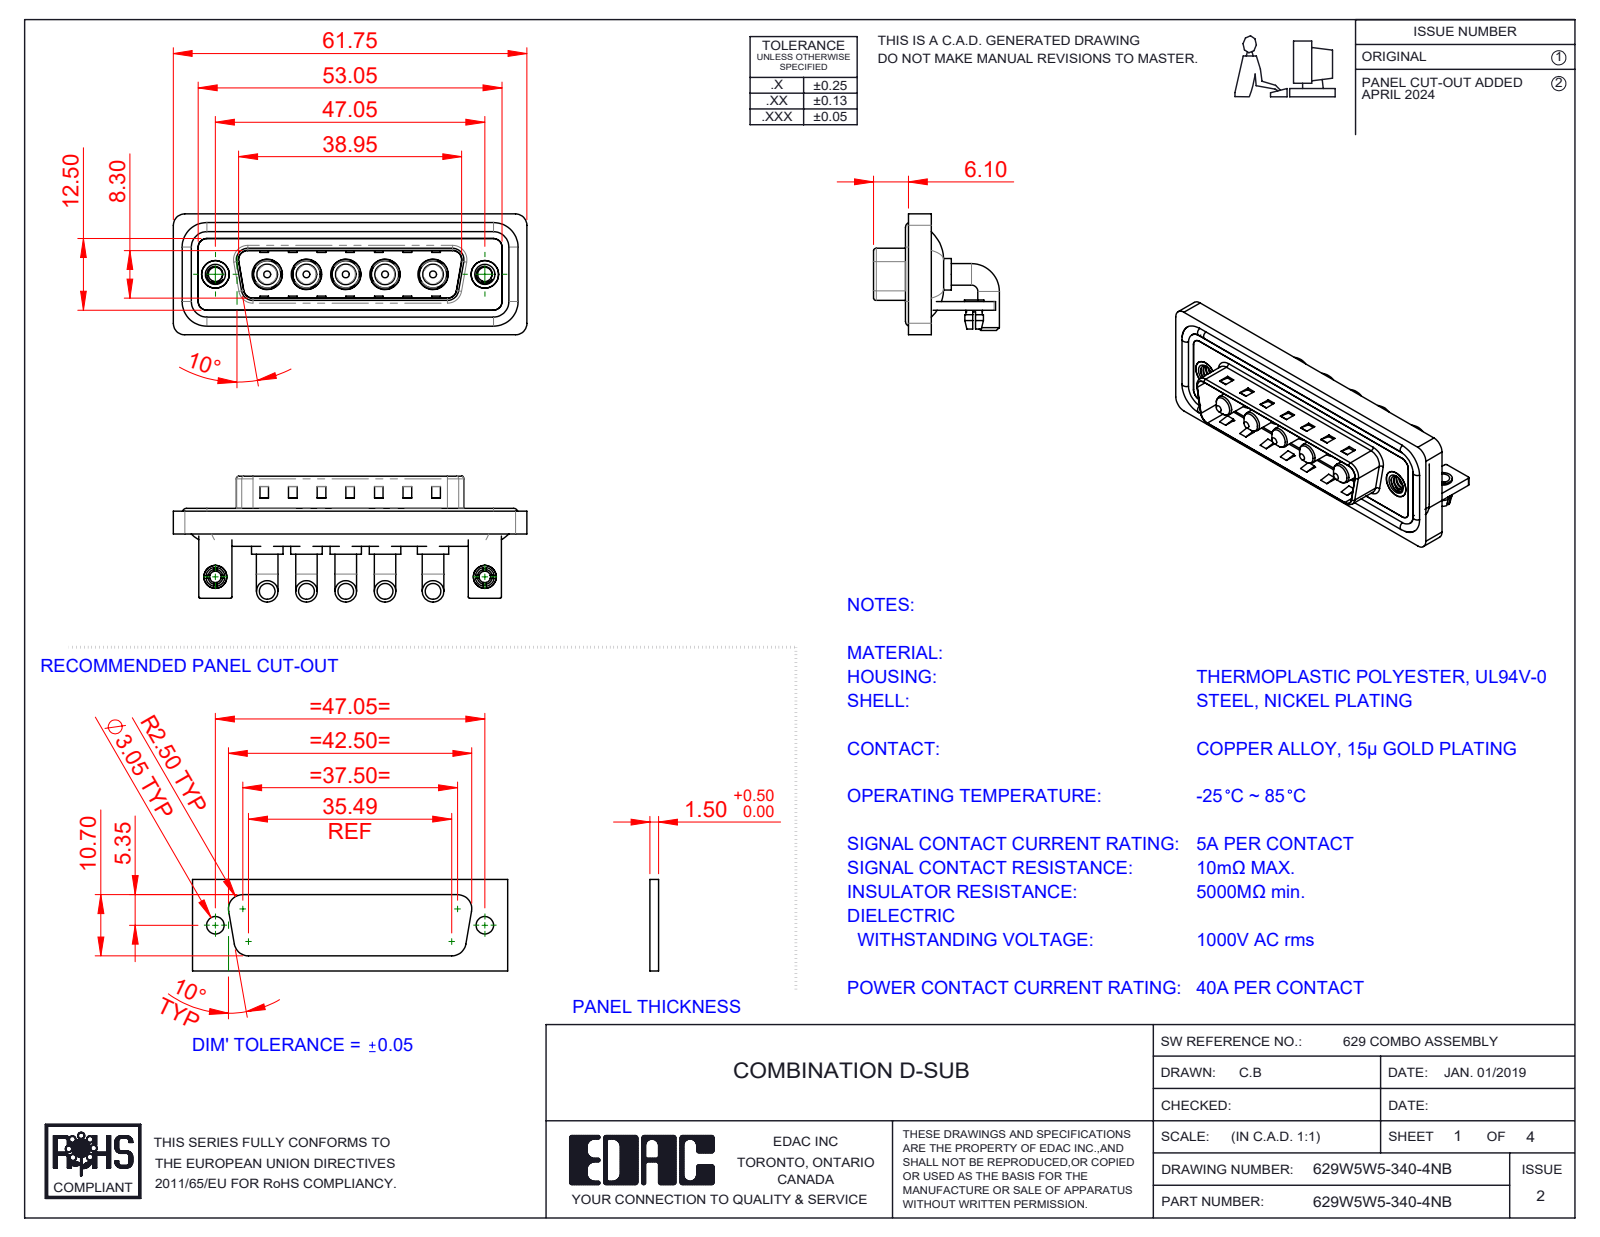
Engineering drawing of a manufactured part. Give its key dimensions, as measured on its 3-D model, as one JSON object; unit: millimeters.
{"part_name": "629Combo Stabilizer Bracket; 629Combo Housing_5W5; 629Combo Waterproof Housing_25 Contacts; 629Combo Shell Rear_25 Contacts (+5 more)", "step_written_by": "SolidWorks 2023 (CONFIG_CONTROL_DESIGN)", "units": "millimeters", "bodies": {"solids": 21, "faces": 828, "planar": 327, "cylindrical": 343, "other": 158}, "overall_size": [61.75, 21.98, 21.1], "volume_mm3": 8475, "surface_area_mm2": 13290, "round_holes": [[4.85, 5], [5.3, 5], [2.5, 4], [2, 2], [3.2, 2], [4, 2], [4.8, 2], [5, 2]], "round_bosses_or_shafts": [[3.75, 10], [5.5, 5], [5.2, 5], [4.75, 5], [3.6, 5], [1.6, 4], [4.9, 2], [4, 2]], "partial_cylinders_radius": [[2, 19], [1.5, 18], [0.25, 16], [0.5, 9], [1.6, 8], [2.1, 5], [0.6, 4], [0.65, 4]], "face_to_face_distances": [0.4, 1.5, 2.9, 0.8, 2.1, 3.7, 1.1, 4.5, 4.1, 1.2], "hole_center_spacings": [6.86, 13.73, 47.05, 6.85, 6.87, 8.37, 8.38, 9.04]}
